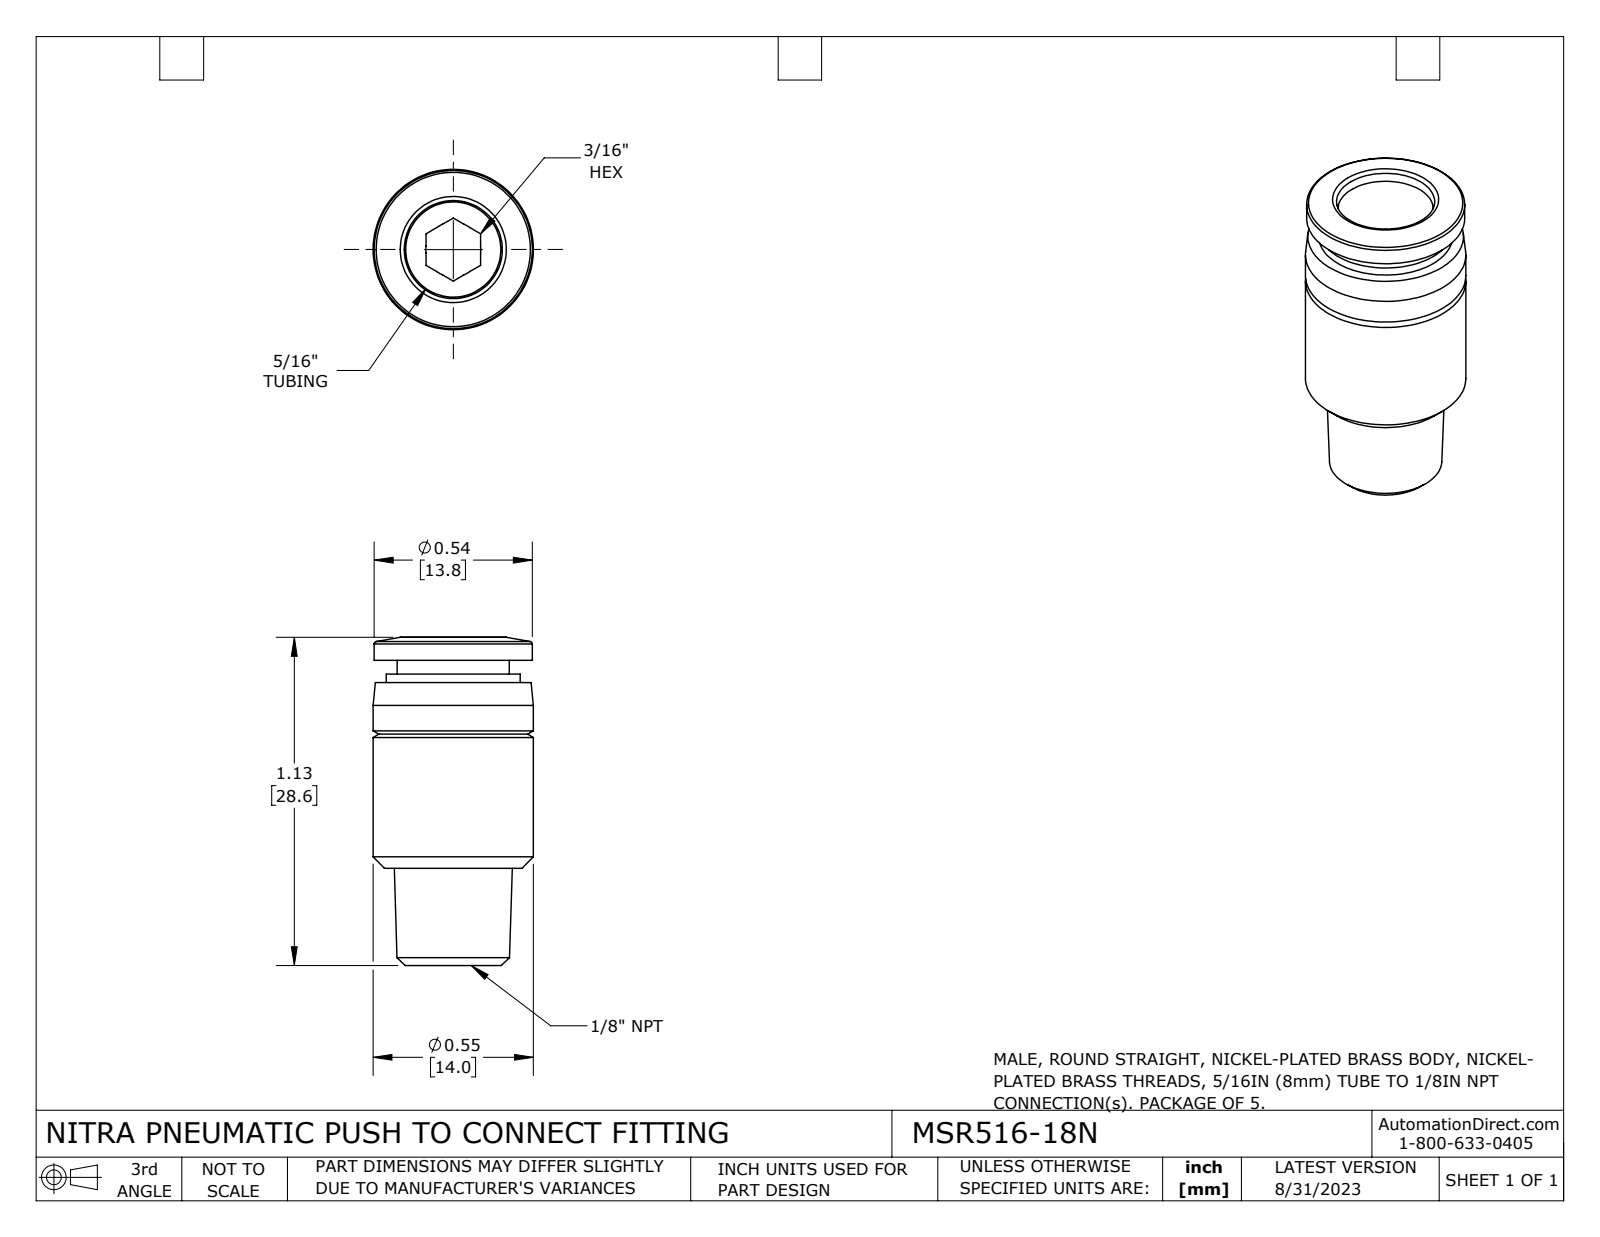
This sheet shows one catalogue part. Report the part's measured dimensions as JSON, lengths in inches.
{"part_name": "MSR516-18N", "step_written_by": "SolidWorks 2019 (AUTOMOTIVE_DESIGN)", "units": "inches", "bodies": {"solids": 1, "faces": 40, "planar": 6, "cylindrical": 14, "other": 20}, "overall_size": [1.128, 0.551, 0.551], "volume_in3": 0.146, "surface_area_in2": 3.299, "round_holes": [[0.189, 1], [0.327, 1]], "round_bosses_or_shafts": [[0.551, 1], [0.543, 1], [0.461, 1], [0.386, 1]], "face_to_face_distances": [0.077, 0.972, 1.049, 0.4, 0.573, 0.65, 1.002, 0.602, 0.03, 0.047]}
